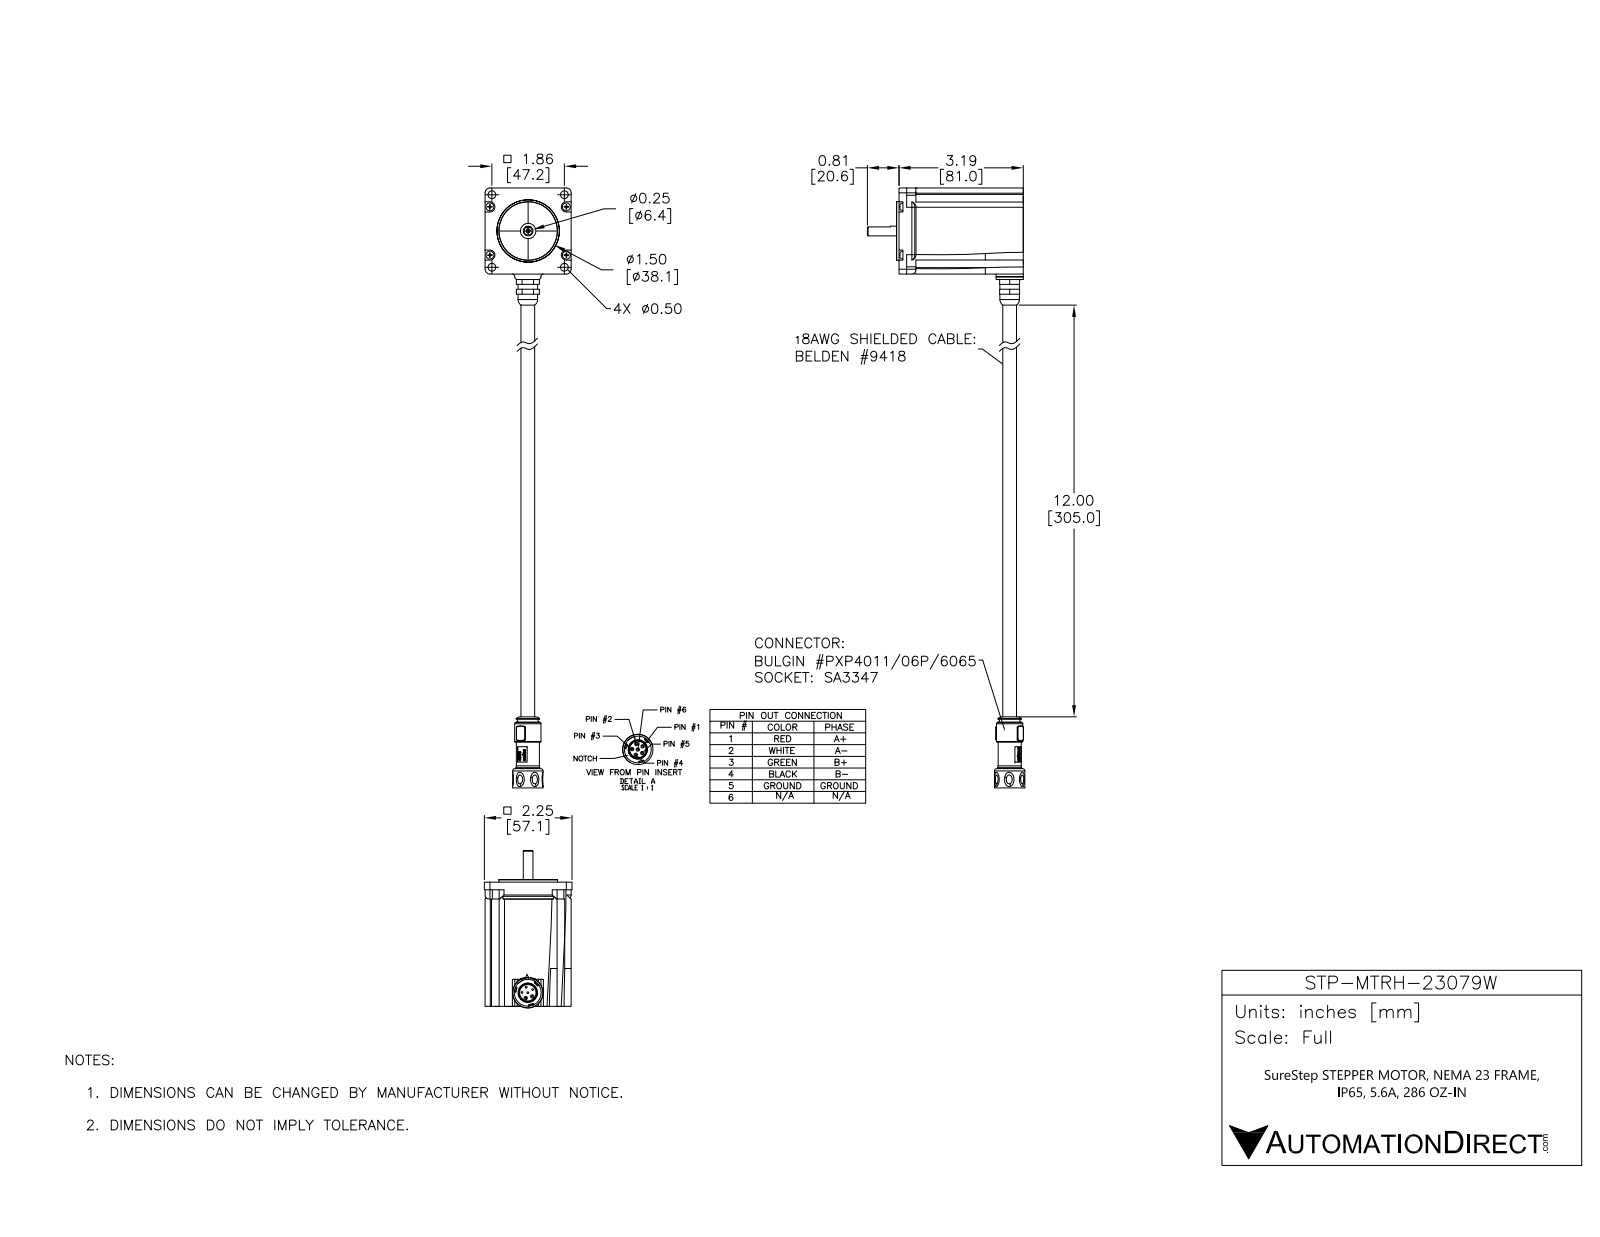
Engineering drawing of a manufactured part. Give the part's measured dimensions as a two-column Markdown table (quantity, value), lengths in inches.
| quantity | value |
| --- | --- |
| part name | STP-MTRH-23079W |
| STEP written by | SolidWorks 2017 (AUTOMOTIVE_DESIGN) |
| units | inches |
| bodies | 3 solids, 897 faces (365 planar, 233 cylindrical, 299 other) |
| overall size | 15.376 × 4.036 × 2.207 |
| volume | 14.54 in³ |
| surface area | 73.25 in² |
| round holes (diameter × count) | 0.047 × 6, 0.097 × 4, 0.2 × 4, 0.125 × 3, 0.125 × 2, 0.063 × 1, 0.228 × 1, 0.394 × 1, 0.398 × 1, 0.449 × 1, 0.467 × 1, 0.689 × 1 |
| round bosses / shafts (diameter × count) | 0.05 × 4, 1.7 × 1, 1.5 × 1, 0.777 × 1, 0.674 × 1, 0.613 × 1, 0.592 × 1, 0.5 × 1 |
| partial cylindrical surfaces (radius × count) | 0.005 × 28, 0.02 × 12, 0.125 × 10, 0.388 × 6, 0.062 × 4, 0.129 × 4, 0.175 × 4, 0.196 × 4 |
| main face-to-face distances | 2.207, 0.314, 2.014, 1.7, 1.171, 1.485, 3.185, 1.174, 1.487, 3.187 |
| hole center spacings | 0.147, 0.148, 0.281, 0.316, 1.181, 1.553, 1.649, 1.661 |
